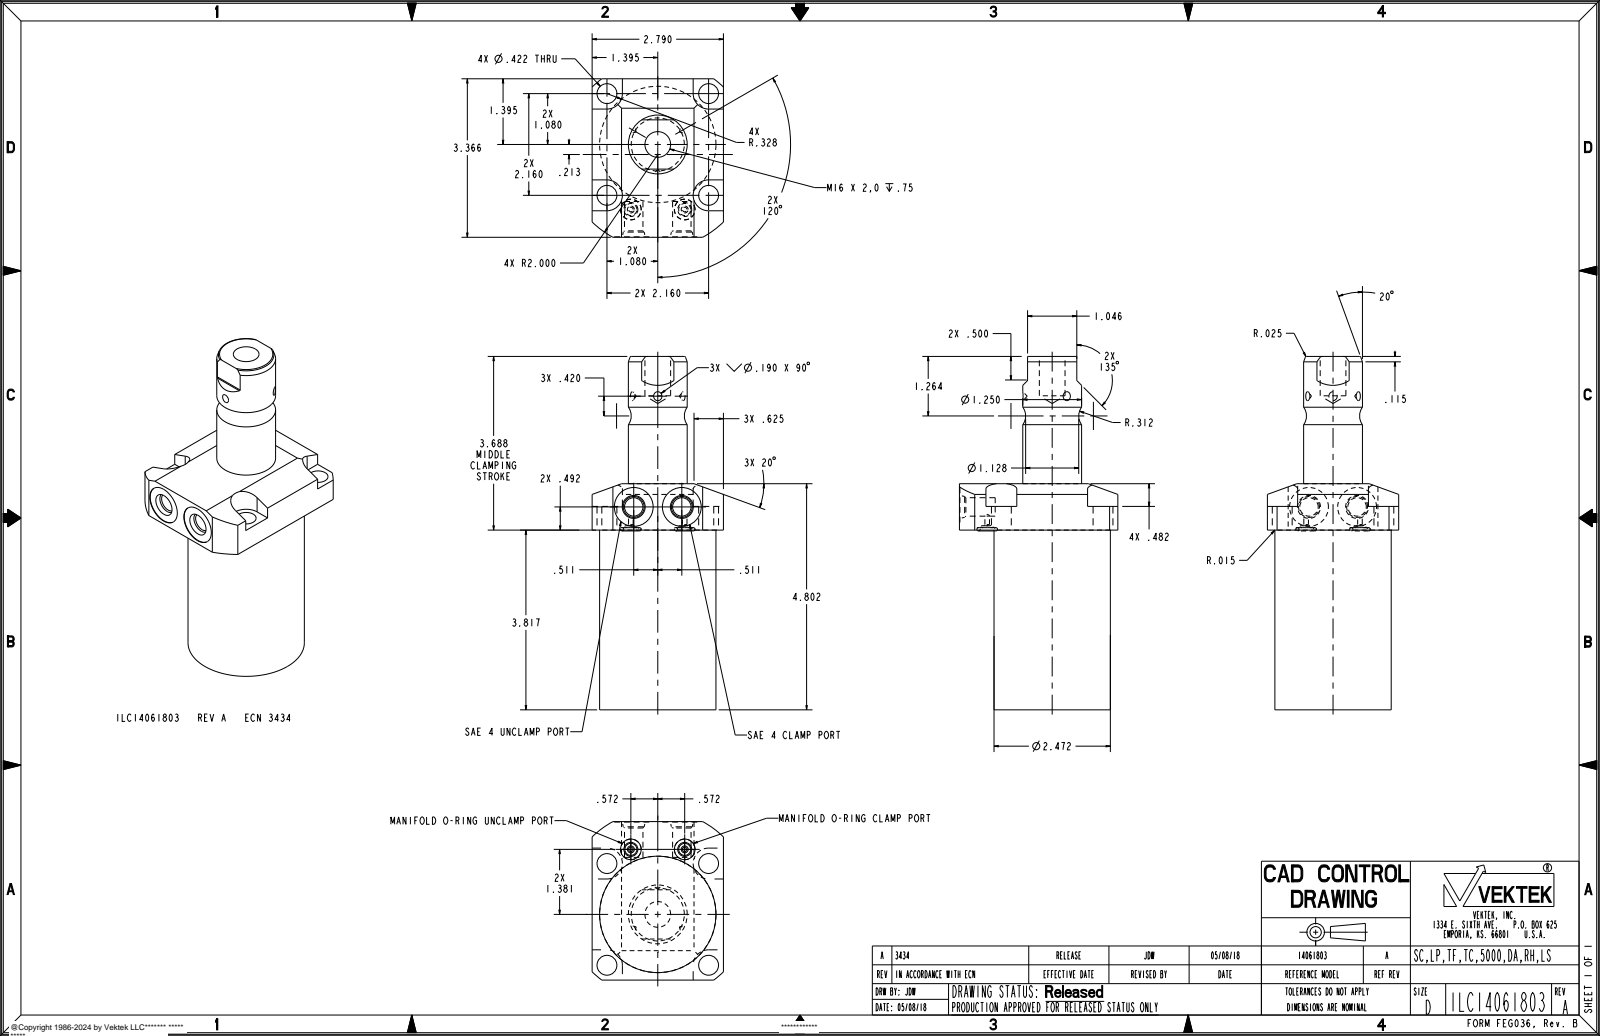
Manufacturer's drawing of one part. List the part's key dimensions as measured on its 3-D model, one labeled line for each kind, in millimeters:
Part name (STEP PRODUCT): ILC14061803
STEP written by: PRO/ENGINEER BY PARAMETRIC TECHNOLOGY CORPORATION, 2013320 (AUTOMOTIVE_DESIGN)
Units: millimetres
Bodies: 3 solids, 119 faces (37 planar, 46 cylindrical, 36 other)
Overall size (bounding box): 190.6 × 85.5 × 70.9
Volume: 471 900 mm³ · Surface area: 48 340 mm²
Round holes (diameter × count): ⌀10.7 ×4, ⌀2.5 ×2, ⌀6.5 ×2, ⌀10 ×2, ⌀11.1 ×2, ⌀21 ×2, ⌀13.9 ×1
Round bosses / shafts (diameter × count): ⌀62.8 ×1, ⌀31.8 ×1
Partial cylindrical surfaces — rounded edges, fillets, slot ends (radius × count): R8.3 ×4, R0.8 ×2, R50.8 ×1
Main face-to-face distances: 97, 122, 25, 70.9, 109.7, 12.8, 12.2, 85.5, 190.6, 93.7
Hole centre spacings: 38.8, 54.9, 15, 38, 42.6, 63.8, 75.3, 77.6
